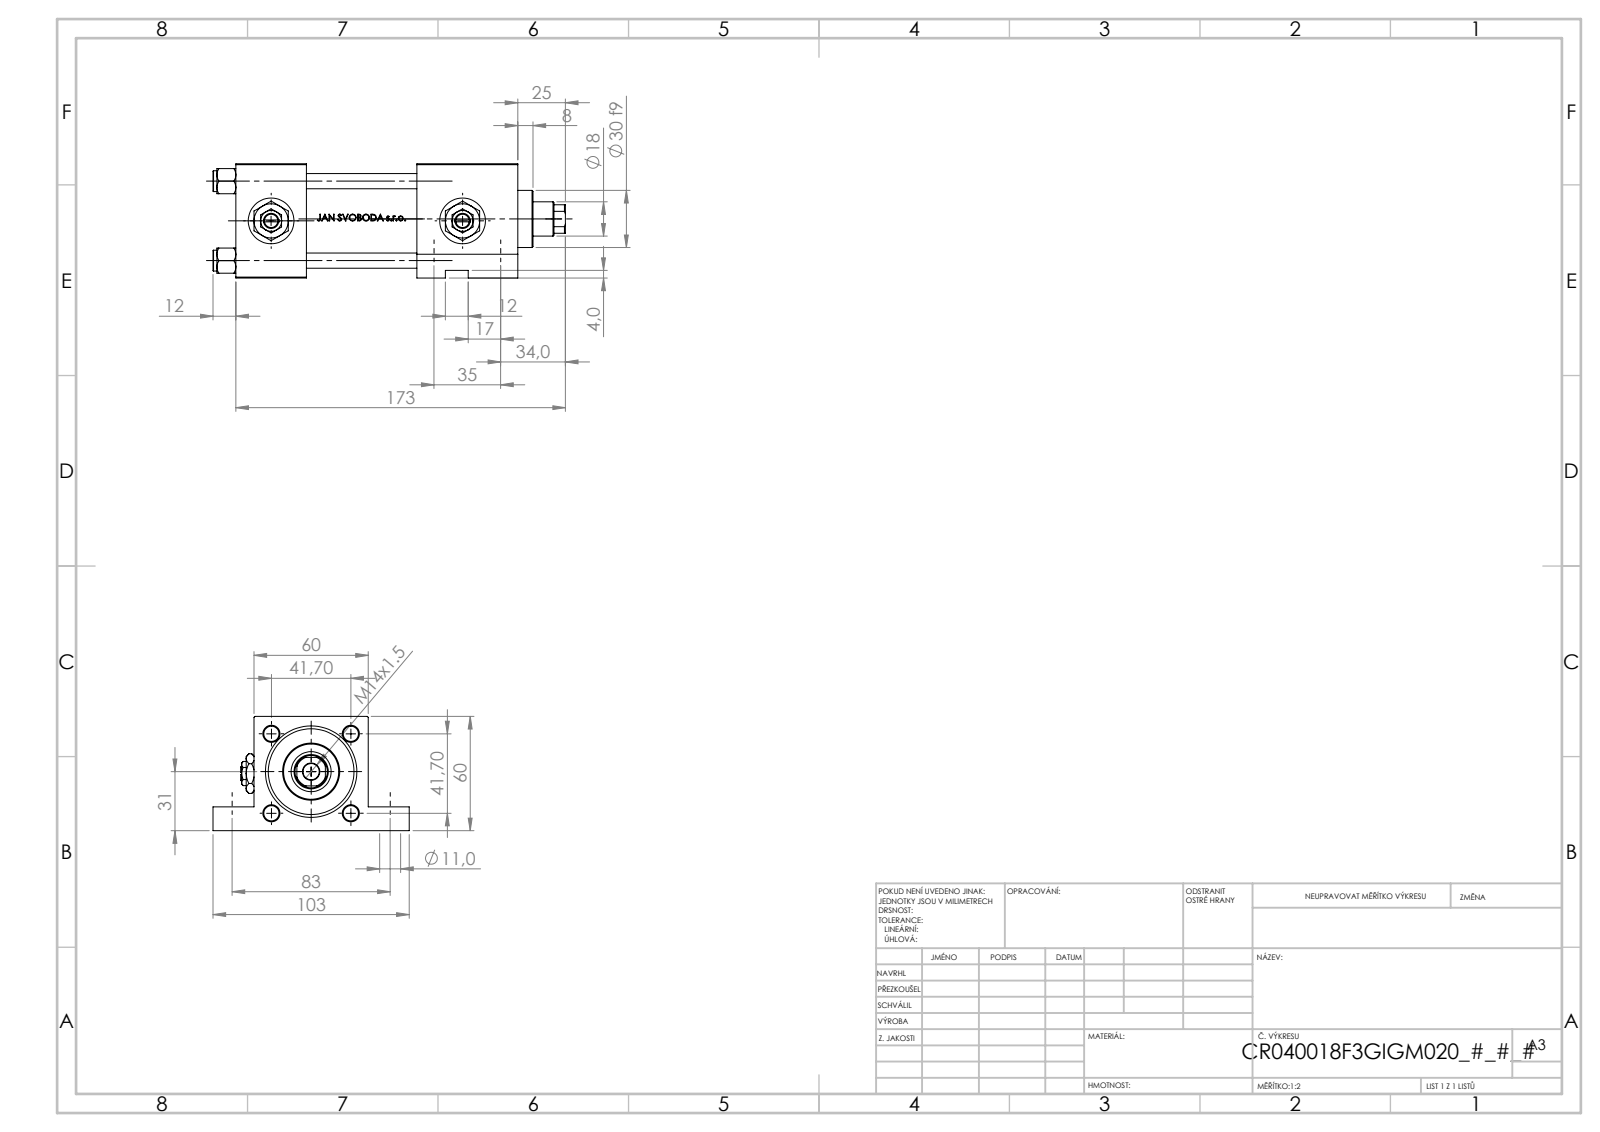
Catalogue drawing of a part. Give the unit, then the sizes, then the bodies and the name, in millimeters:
Units: millimetres
Overall size (bounding box): 185 × 103 × 60
Round holes (diameter × count): ⌀8 ×4, ⌀16.66 ×3, ⌀24 ×3, ⌀7 ×2, ⌀11 ×2, ⌀11 ×2, ⌀8.5 ×1, ⌀16 ×1, ⌀18 ×1, ⌀21 ×1, ⌀31 ×1, ⌀40 ×1
Round bosses / shafts (diameter × count): ⌀11 ×4, ⌀46 ×1, ⌀30 ×1
Partial cylindrical surfaces — rounded edges, fillets, slot ends (radius × count): R8.5 ×1
Main face-to-face distances: 60, 37, 148, 111, 53, 58, 95, 119.3, 82.3, 24.3
Hole centre spacings: 41.7, 28.79, 30.2, 35, 42.09, 50.06, 58.97, 83
Volume: 420 373 mm³ · Surface area: 114 469 mm²
Bodies: 13 solids, 1215 faces (484 planar, 149 cylindrical, 582 other)
Part name (STEP PRODUCT): V215_VC_A; NUT_M5_F; V215CR_F_Body; Zatka_pro_OIL_PORT (+2 more)
STEP written by: SolidWorks 2019 (CONFIG_CONTROL_DESIGN)
